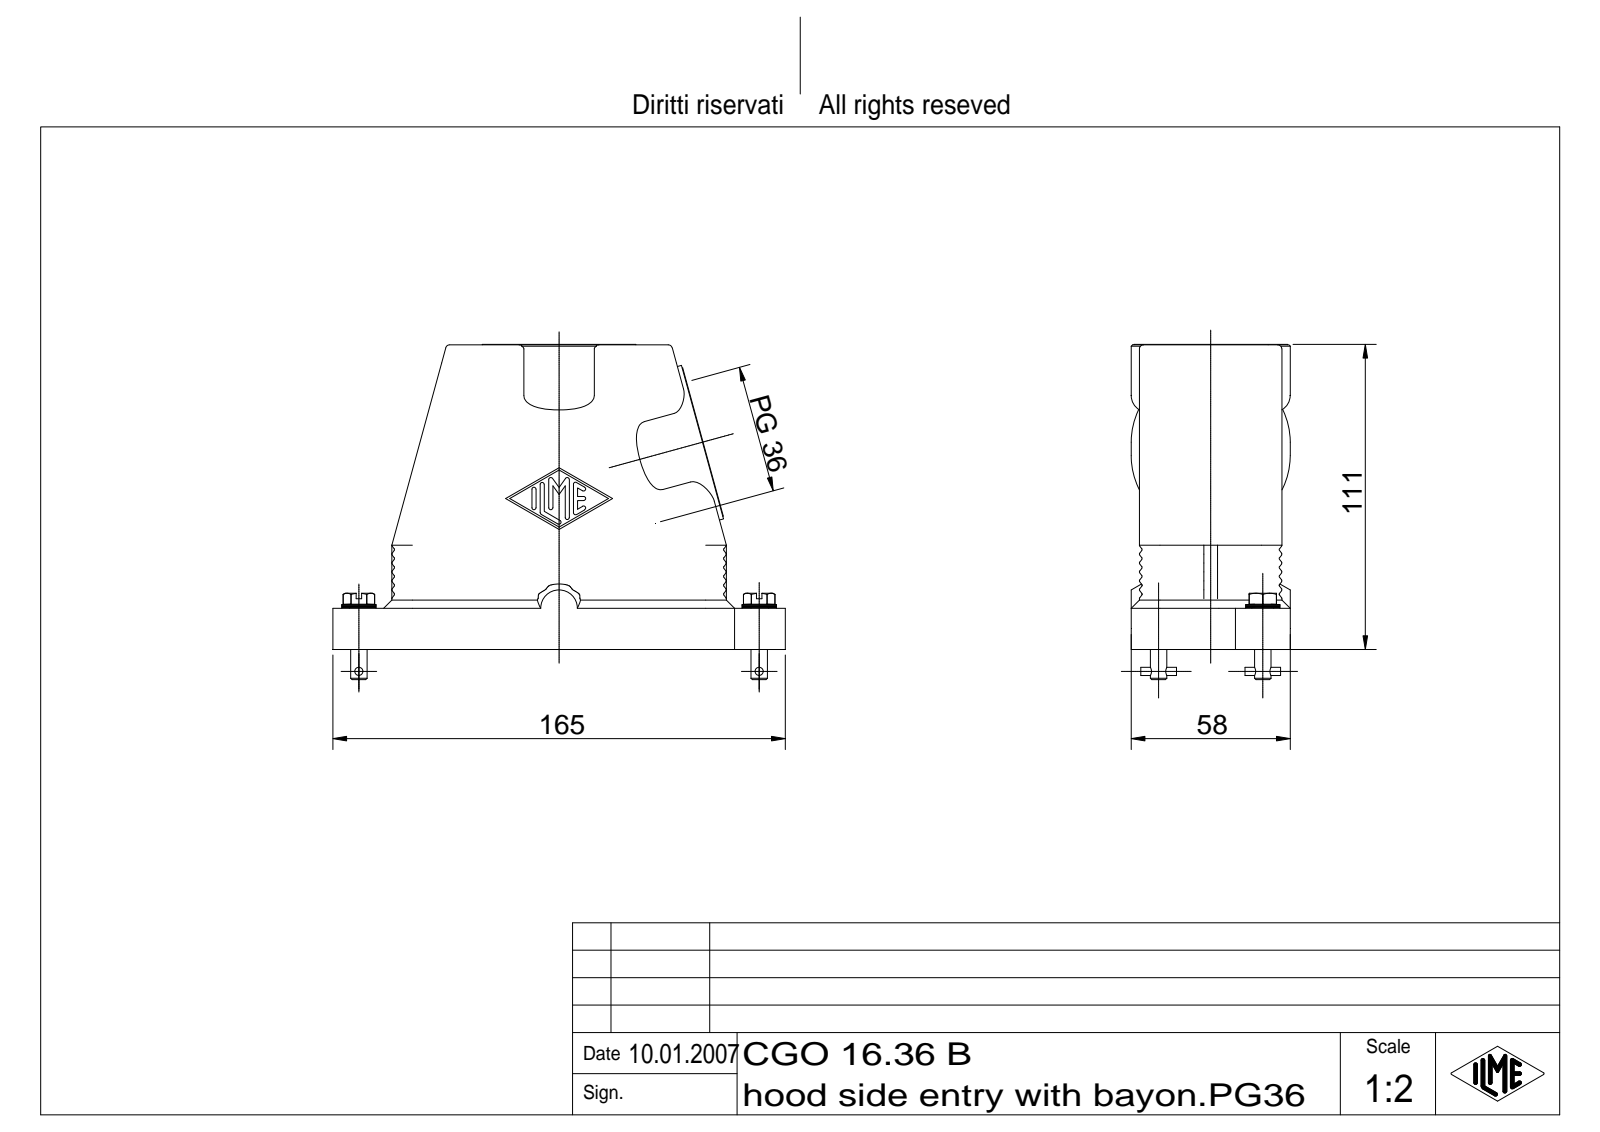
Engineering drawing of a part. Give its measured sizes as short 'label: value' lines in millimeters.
name: CGO 16.36 B
written by: Autodesk Inventor 7 (AUTOMOTIVE_DESIGN)
unit: mm
bodies: 3 solids, 780 faces (194 planar, 203 cylindrical, 383 other)
size: 165 × 122.2 × 58
volume: 212 321 mm³; area: 91 171 mm²
holes: 2× ⌀2.46, 2× ⌀3.2, 2× ⌀6.6, 2× ⌀15, 1× ⌀45.48
bosses: 2× ⌀58, 2× ⌀56, 2× ⌀12.5, 2× ⌀6, 2× ⌀3
rounds: 39× R0.5, 14× R0.75, 8× R7.5, 6× R6, 4× R1.5, 4× R3, 2× R5.75, 2× R10.5
face distances: 3, 52, 49, 6, 46, 55, 2.5, 0.5, 58, 3.5
hole spacings: 34.69, 116.38, 82.07, 150.86
